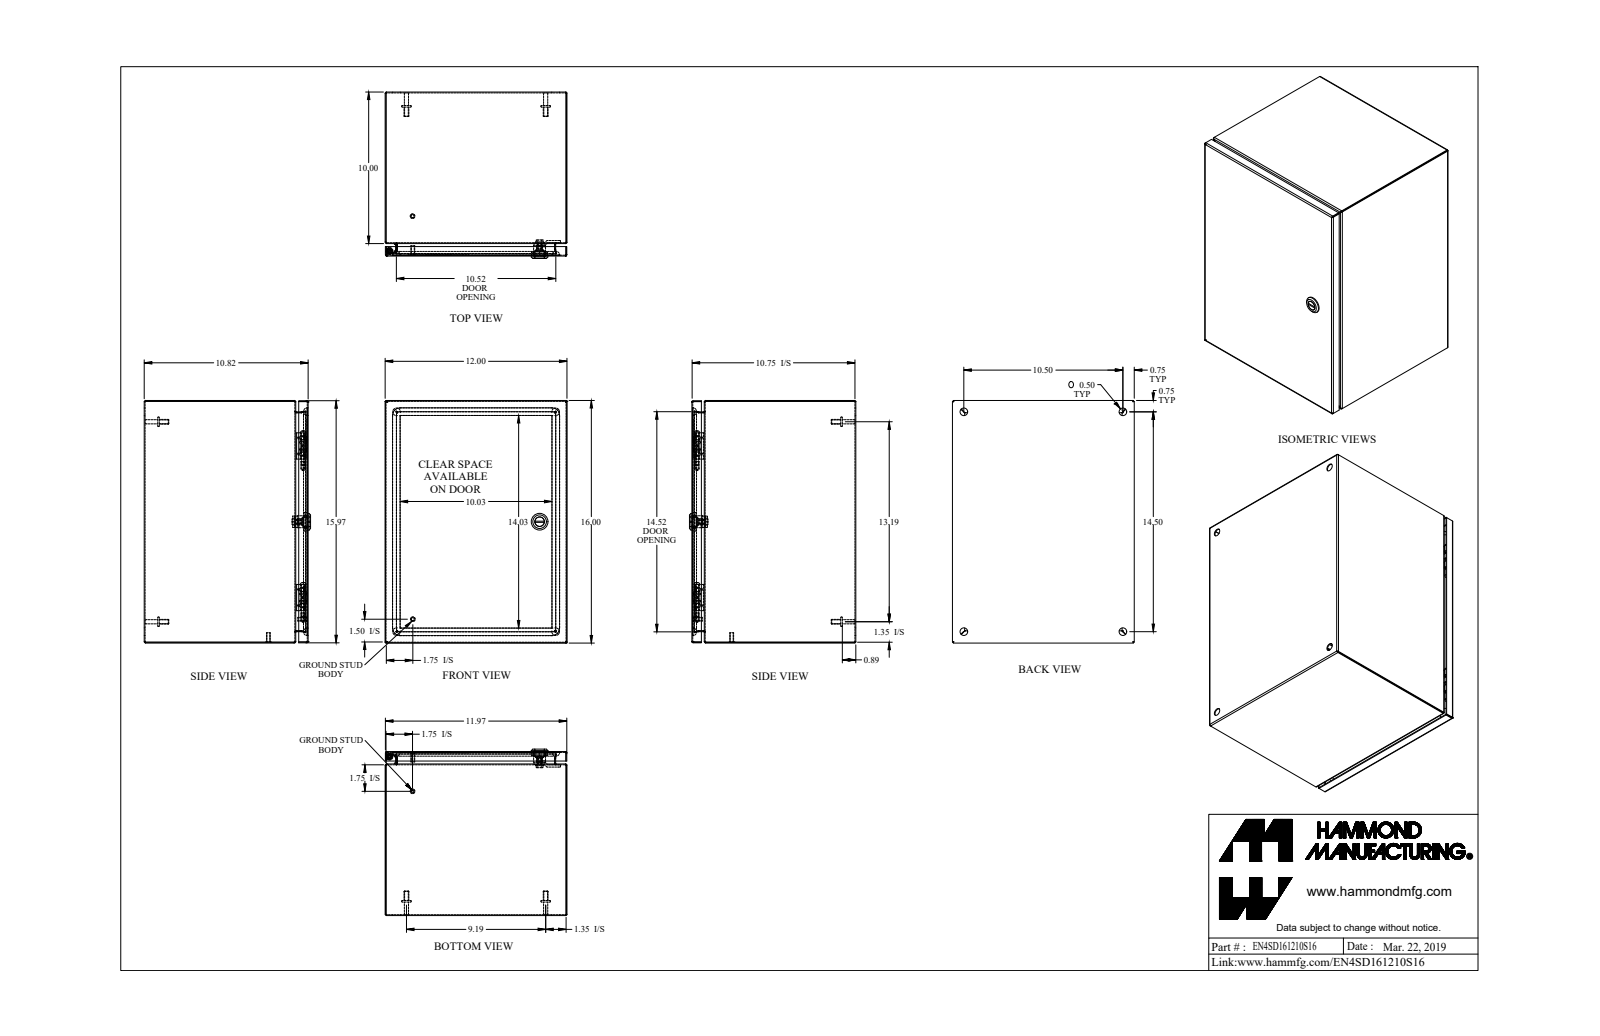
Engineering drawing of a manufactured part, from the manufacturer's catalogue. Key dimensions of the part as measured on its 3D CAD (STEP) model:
Part name (STEP PRODUCT): EN4SD161210S16_Default
STEP written by: SolidWorks 2019 (CONFIG_CONTROL_DESIGN)
Units: inches
Bodies: 22 solids, 657 faces (303 planar, 212 cylindrical, 142 other)
Overall size (bounding box): 16 × 12 × 10.981
Volume: 65.7 in³ · Surface area: 2 234 in²
Round holes (diameter × count): ⌀0.5 ×5, ⌀0.172 ×1, ⌀0.197 ×1, ⌀0.24 ×1, ⌀0.242 ×1, ⌀0.387 ×1, ⌀0.63 ×1, ⌀0.768 ×1
Round bosses / shafts (diameter × count): ⌀0.313 ×6, ⌀0.625 ×5, ⌀0.275 ×4, ⌀0.25 ×2, ⌀1.1 ×1, ⌀0.785 ×1, ⌀0.525 ×1, ⌀0.475 ×1
Partial cylindrical surfaces — rounded edges, fillets, slot ends (radius × count): R0.029 ×21, R0.086 ×21, R0.188 ×12, R0.006 ×4, R0.062 ×4, R0.25 ×4, R0.499 ×4, R0.125 ×2
Main face-to-face distances: 0.057, 11.943, 15.943, 0.057, 10.707, 10.764, 10.764, 10.821, 11.886, 12
Hole centre spacings: 7.327, 10.5, 11.904, 14.5, 17.902
